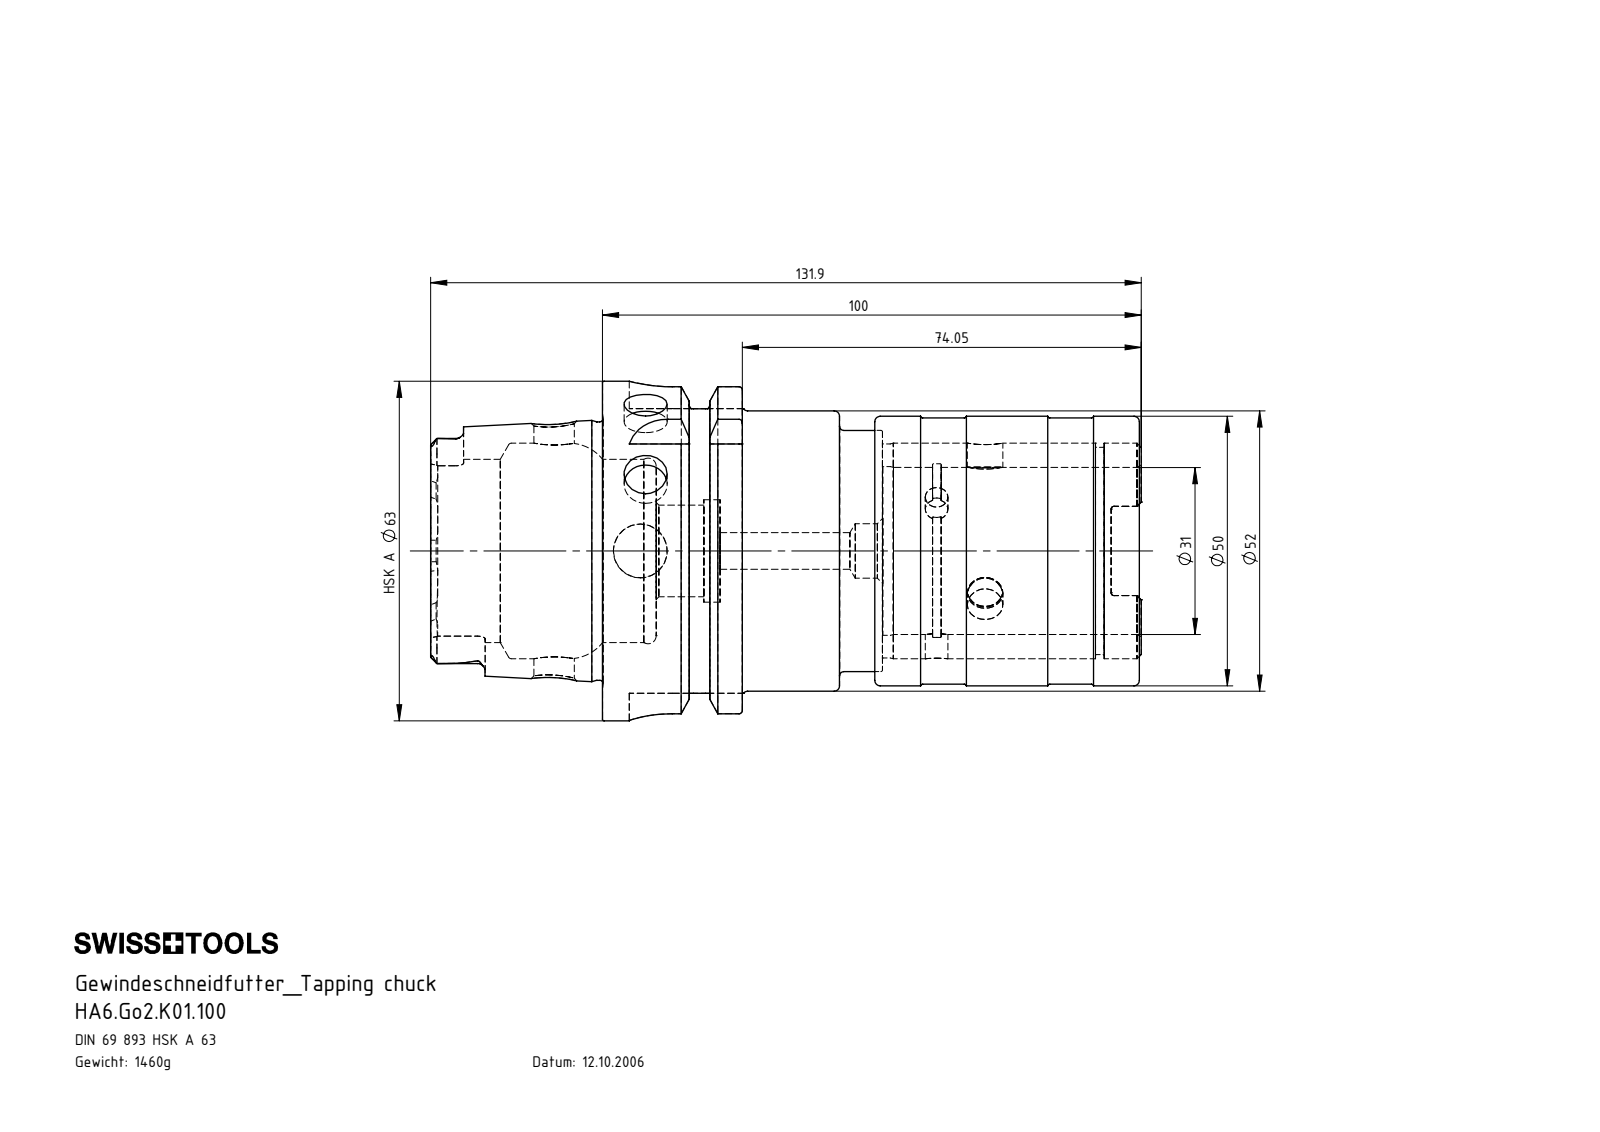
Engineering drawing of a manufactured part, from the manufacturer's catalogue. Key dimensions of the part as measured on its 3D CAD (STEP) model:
Part name (STEP PRODUCT): HA6.Go2.K01.100; Einbausatz Go2_gespannt; Kugel Go2; Hülse Go2 (+6 more)
STEP written by: SolidWorks 2011 (AUTOMOTIVE_DESIGN)
Units: millimetres
Bodies: 10 solids, 394 faces (91 planar, 121 cylindrical, 182 other)
Overall size (bounding box): 131.9 × 63 × 63
Volume: 185 918 mm³ · Surface area: 61 213 mm²
Round holes (diameter × count): ⌀4.2 ×3, ⌀6.6 ×3, ⌀8 ×2, ⌀2.5 ×1, ⌀6.8 ×1, ⌀7.5 ×1, ⌀10 ×1, ⌀10.1 ×1, ⌀17 ×1, ⌀19 ×1, ⌀31 ×1, ⌀31.3 ×1
Round bosses / shafts (diameter × count): ⌀63 ×1, ⌀54.95 ×1, ⌀52 ×1, ⌀50 ×1, ⌀49.4 ×1, ⌀47.94 ×1, ⌀44.75 ×1, ⌀40 ×1
Partial cylindrical surfaces — rounded edges, fillets, slot ends (radius × count): R1.4 ×6, R2.88 ×4, R8 ×4, R3.1 ×3, R0.5 ×2
Main face-to-face distances: 16, 64.65, 40.6, 52, 12.65, 25.95, 26.05, 38.7, 52.65, 26.7
Hole centre spacings: 9, 71, 80
